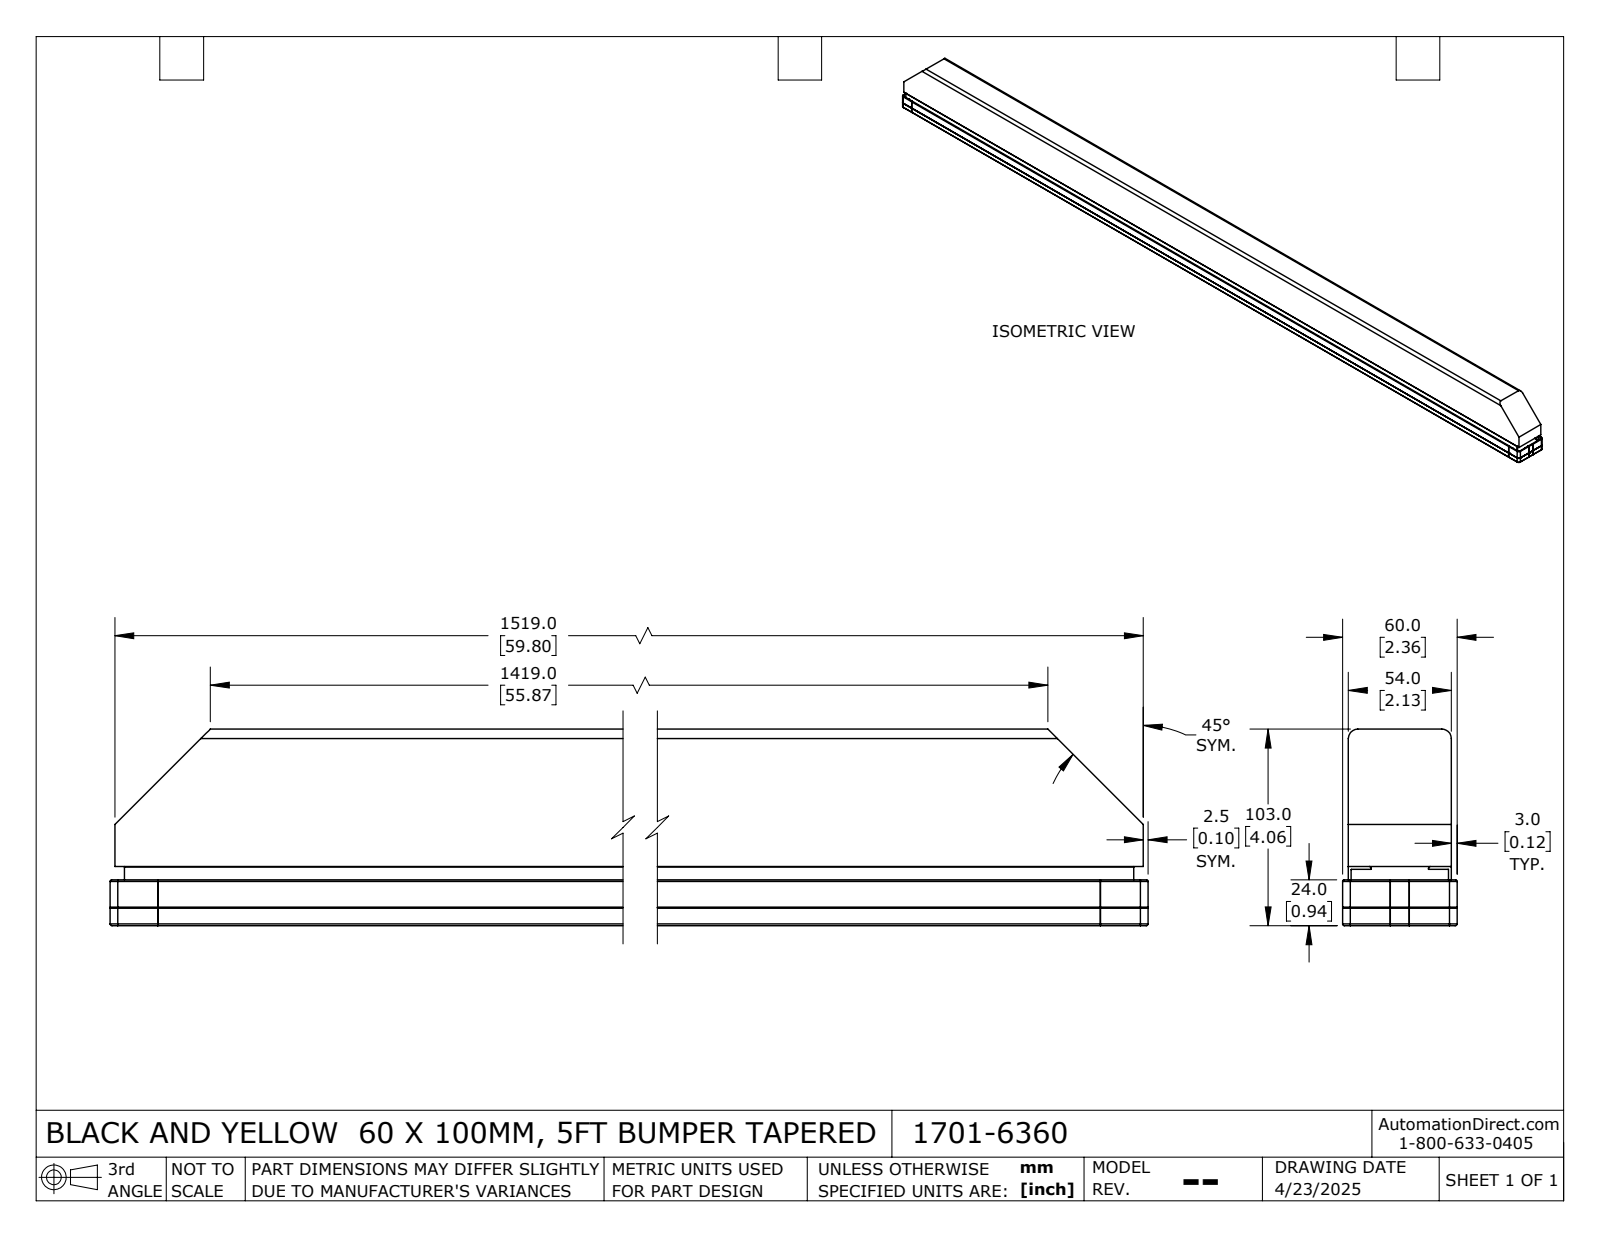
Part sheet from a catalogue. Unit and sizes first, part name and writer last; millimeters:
Units: millimetres
Overall size (bounding box): 1524 × 103 × 60
Partial cylindrical surfaces — rounded edges, fillets, slot ends (radius × count): R0.1 ×160, R0.2 ×14, R1 ×10, R0.3 ×8, R0.5 ×8, R0.8 ×8, R4 ×6, R2.8 ×4
Main face-to-face distances: 2, 54, 14, 1.5, 3, 15.5, 13.5, 12, 4.5, 52.5
Volume: 6 511 000 mm³ · Surface area: 1 245 000 mm²
Bodies: 11 solids, 1636 faces (886 planar, 718 cylindrical, 32 other)
Part name (STEP PRODUCT): 17-005394-00-c
STEP written by: SolidWorks 2024 (AUTOMOTIVE_DESIGN)
